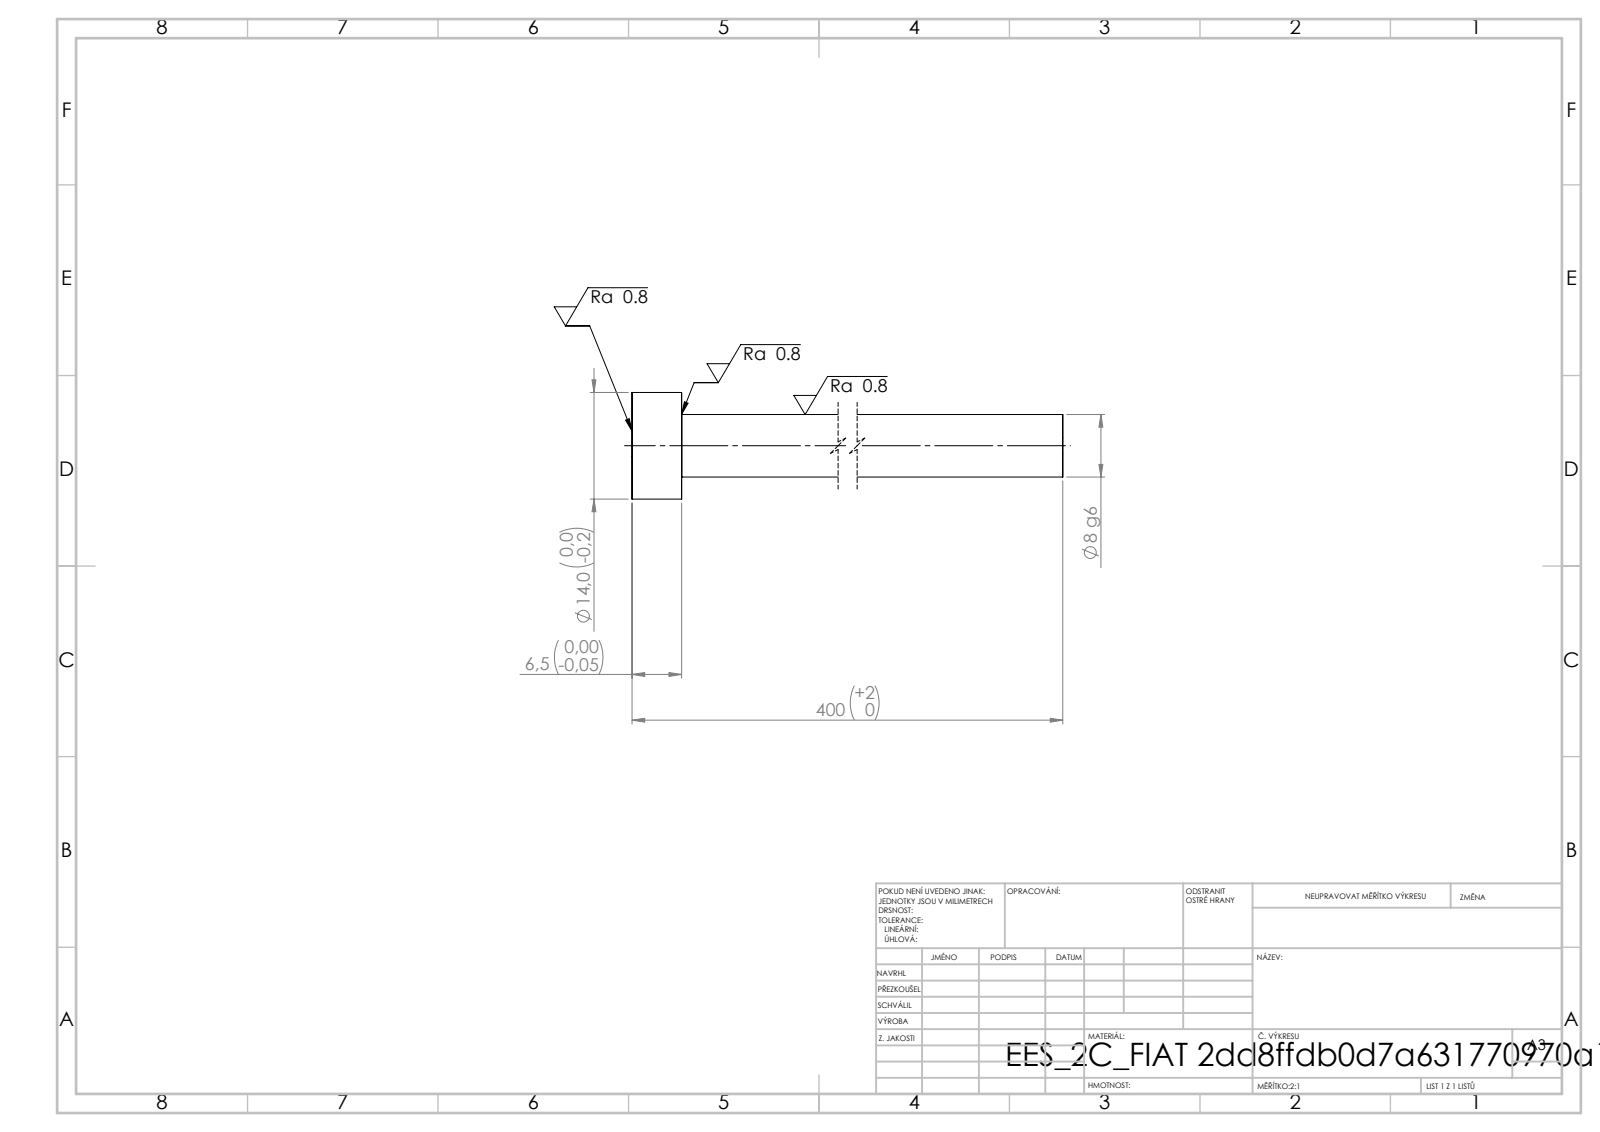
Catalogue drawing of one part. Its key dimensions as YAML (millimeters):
step_written_by: "SolidWorks 2019 (CONFIG_CONTROL_DESIGN)"
units: millimeters
bodies: {solids: 1, faces: 7, planar: 3, cylindrical: 4, other: 0}
overall_size: [400, 14, 14]
volume: 21781
surface_area: 10731
round_bosses_or_shafts:
  - {diameter: 14, count: 1}
  - {diameter: 8.2, count: 1}
face_to_face_distances: [6.5, 400, 393.5]
